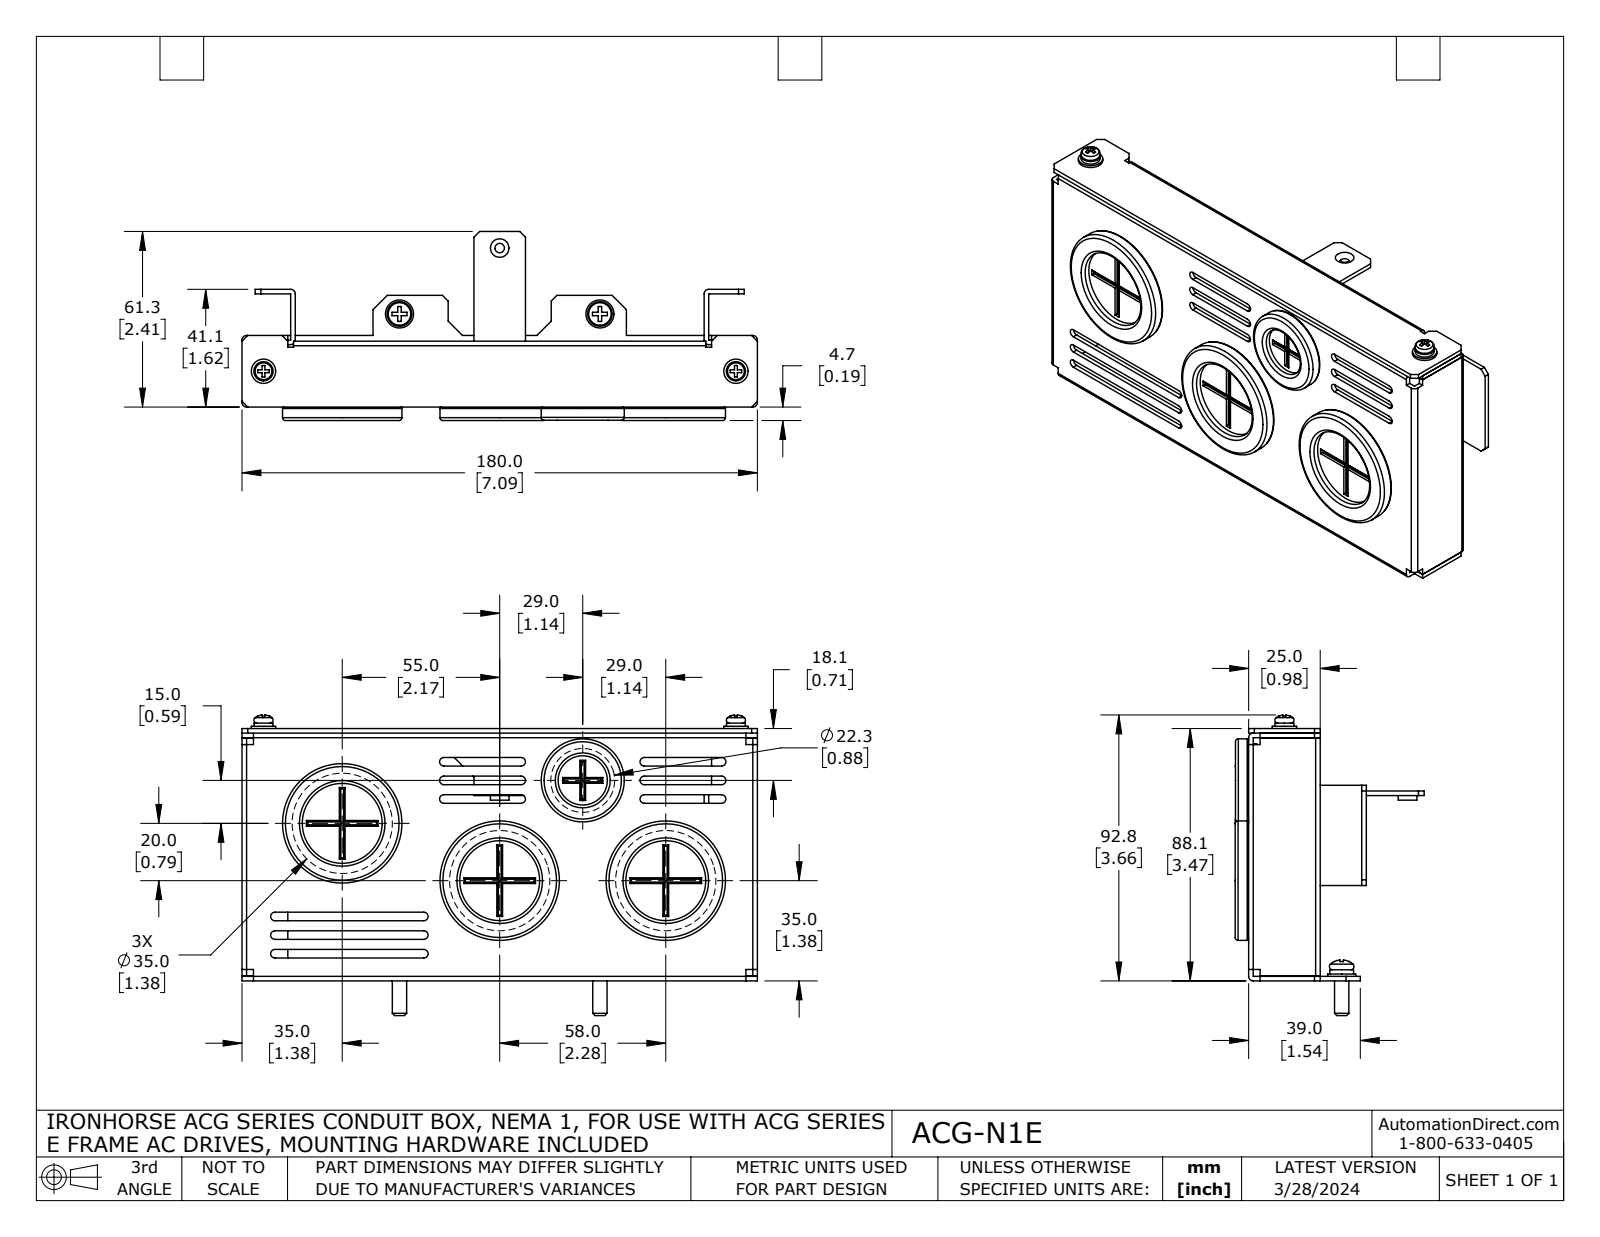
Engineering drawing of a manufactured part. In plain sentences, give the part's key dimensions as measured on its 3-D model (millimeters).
The part is named "ACG-N1E". Its 3-D file was written by "SolidWorks 2021 (AUTOMOTIVE_DESIGN)". It is 12 solids with 598 faces: 311 planar, 205 cylindrical and 82 other. Overall it measures 180 by 105 by 66 millimeters. Its volume is 84 720 cubic millimeters and its surface area 96 450 square millimeters. Round holes: 4 of diameter 3, 4 of diameter 3.2, 3 of diameter 27.9, 3 of diameter 35, 3 of diameter 38.7, 2 of diameter 3.3, 2 of diameter 4.5, 2 of diameter 6, 1 of diameter 3.4, 1 of diameter 17.2, 1 of diameter 22.3, 1 of diameter 26. Round bosses or shafts: 3 of diameter 41.7, 3 of diameter 37.7, 3 of diameter 34.3, 2 of diameter 9.8, 2 of diameter 8.5, 2 of diameter 8.3, 2 of diameter 6.6, 2 of diameter 6.5. Partial cylindrical surfaces (rounded edges, fillets, slot ends): 28 of radius 0.5, 18 of radius 1.5, 12 of radius 1.6, 2 of radius 3. The main face-to-face distances are 1.6, 86.5, 84.9, 23.4, 21.8, 3.2, 88.1, 178.4, 0.8, 2. The hole center spacings are 20, 41.9, 45.4, 51.5, 80.2, 84, 93, 119.2.
